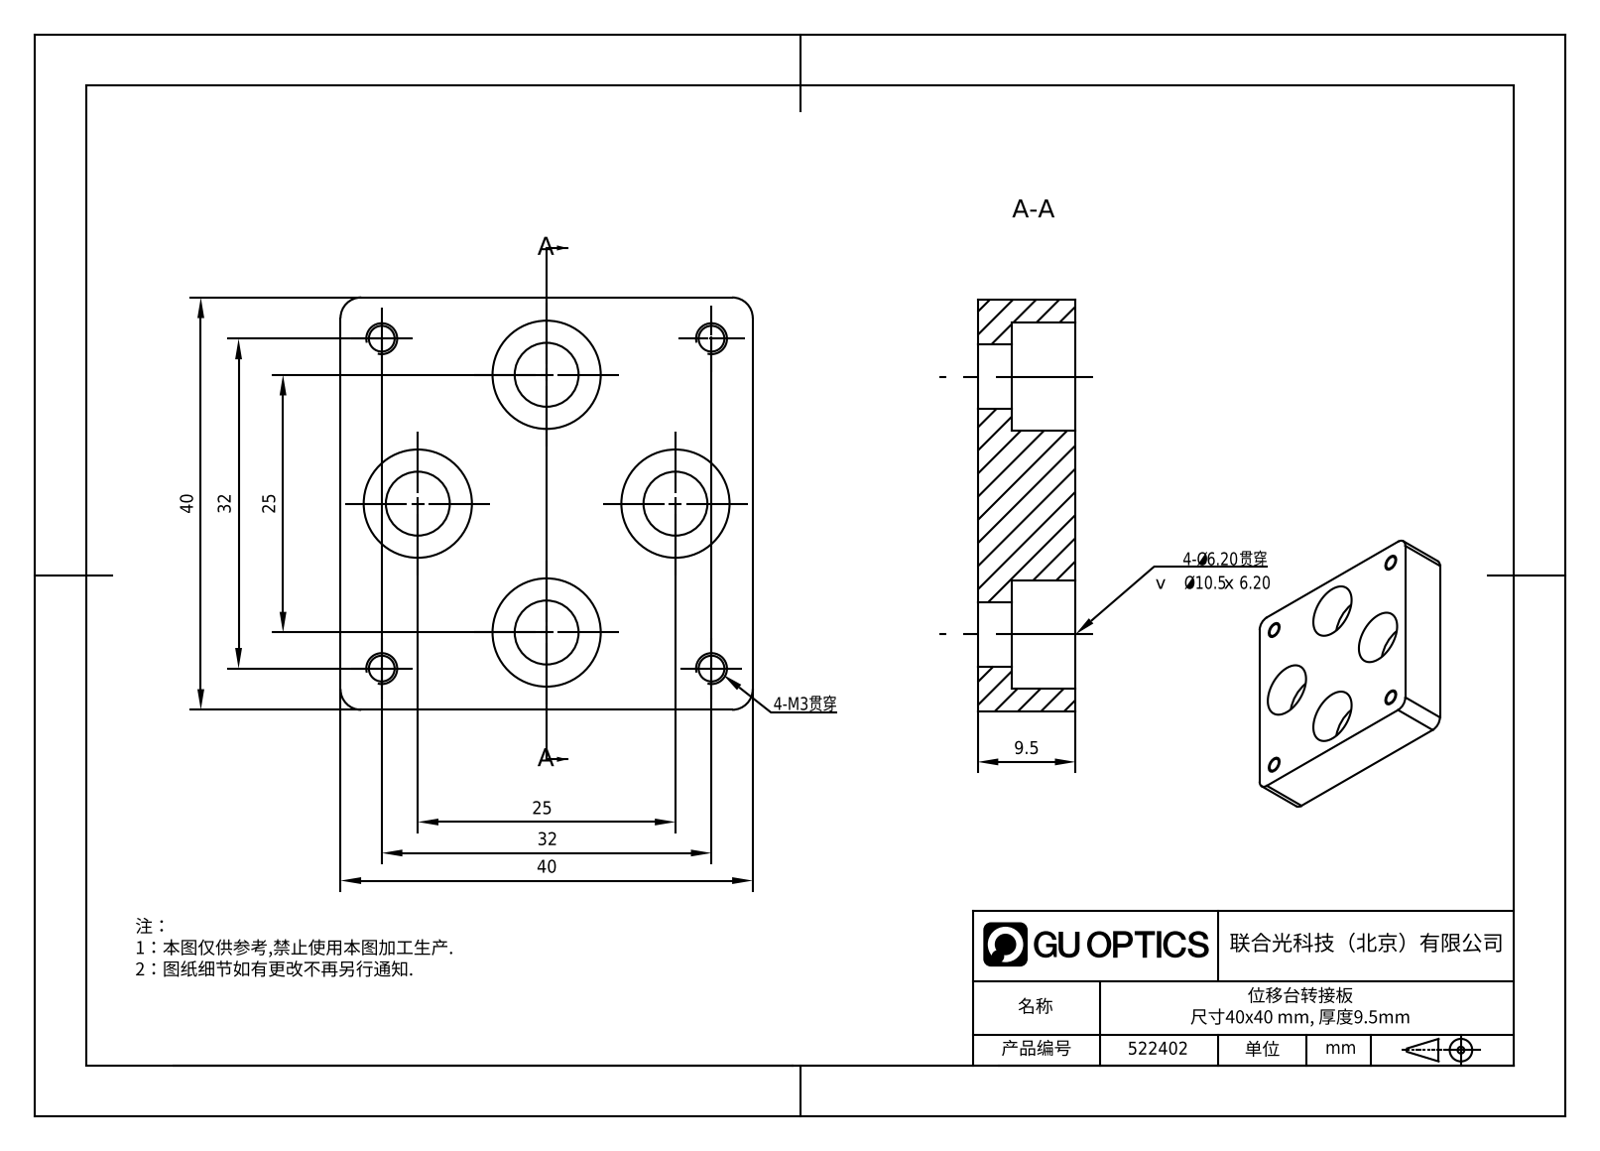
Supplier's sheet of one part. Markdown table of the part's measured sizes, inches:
| quantity | value |
| --- | --- |
| part name | 522402 |
| STEP written by | SolidWorks 2020 (CONFIG_CONTROL_DESIGN) |
| units | inches |
| bodies | 1 solid, 38 faces (10 planar, 28 cylindrical, 0 other) |
| overall size | 1.575 × 1.575 × 0.374 |
| volume | 0.759 in³ |
| surface area | 8.948 in² |
| round holes (diameter × count) | 0.098 × 4, 0.244 × 4, 0.413 × 4 |
| partial cylindrical surfaces (radius × count) | 0.079 × 4 |
| main face-to-face distances | 0.374, 1.575, 0.13, 0.244 |
| hole center spacings | 0.645, 1.287, 0.696, 1.26, 0.984, 1.781 |
